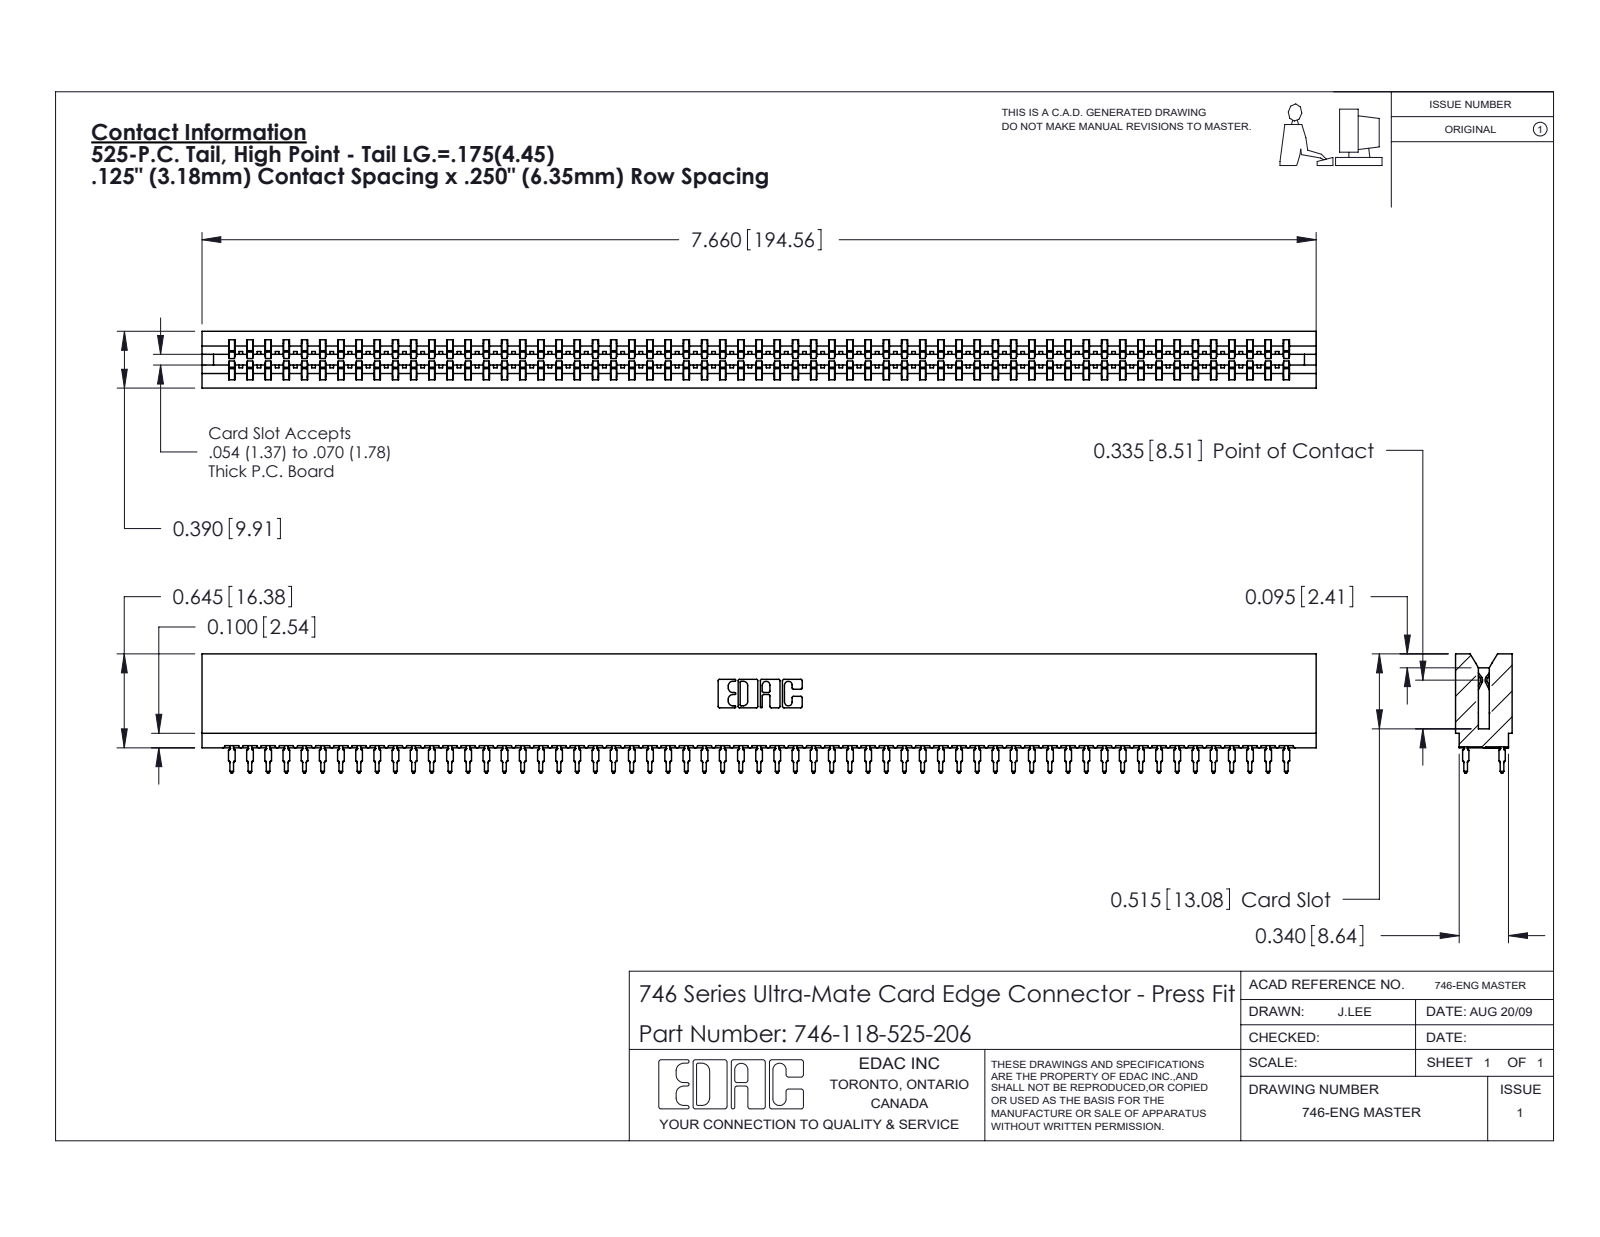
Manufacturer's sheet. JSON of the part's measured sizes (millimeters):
{"part_name": "746 Part_.515 Slot Depth - 06; 746-292-001_525; 746-118-525-206", "step_written_by": "SolidWorks 2020 (CONFIG_CONTROL_DESIGN)", "units": "millimeters", "bodies": {"solids": 119, "faces": 10659, "planar": 5484, "cylindrical": 2107, "other": 3068}, "overall_size": [194.6, 20.8, 9.9], "volume_mm3": 20660, "surface_area_mm2": 33240, "partial_cylinders_radius": [[0.5, 236], [0.4, 60], [0.3, 22], [0.1, 8], [0.3, 8], [0.2, 6], [0.8, 6], [0.7, 3]], "face_to_face_distances": [1.4, 8.5, 9.9, 6.4, 0.6, 7.8, 7, 2.1, 4.4, 4]}
